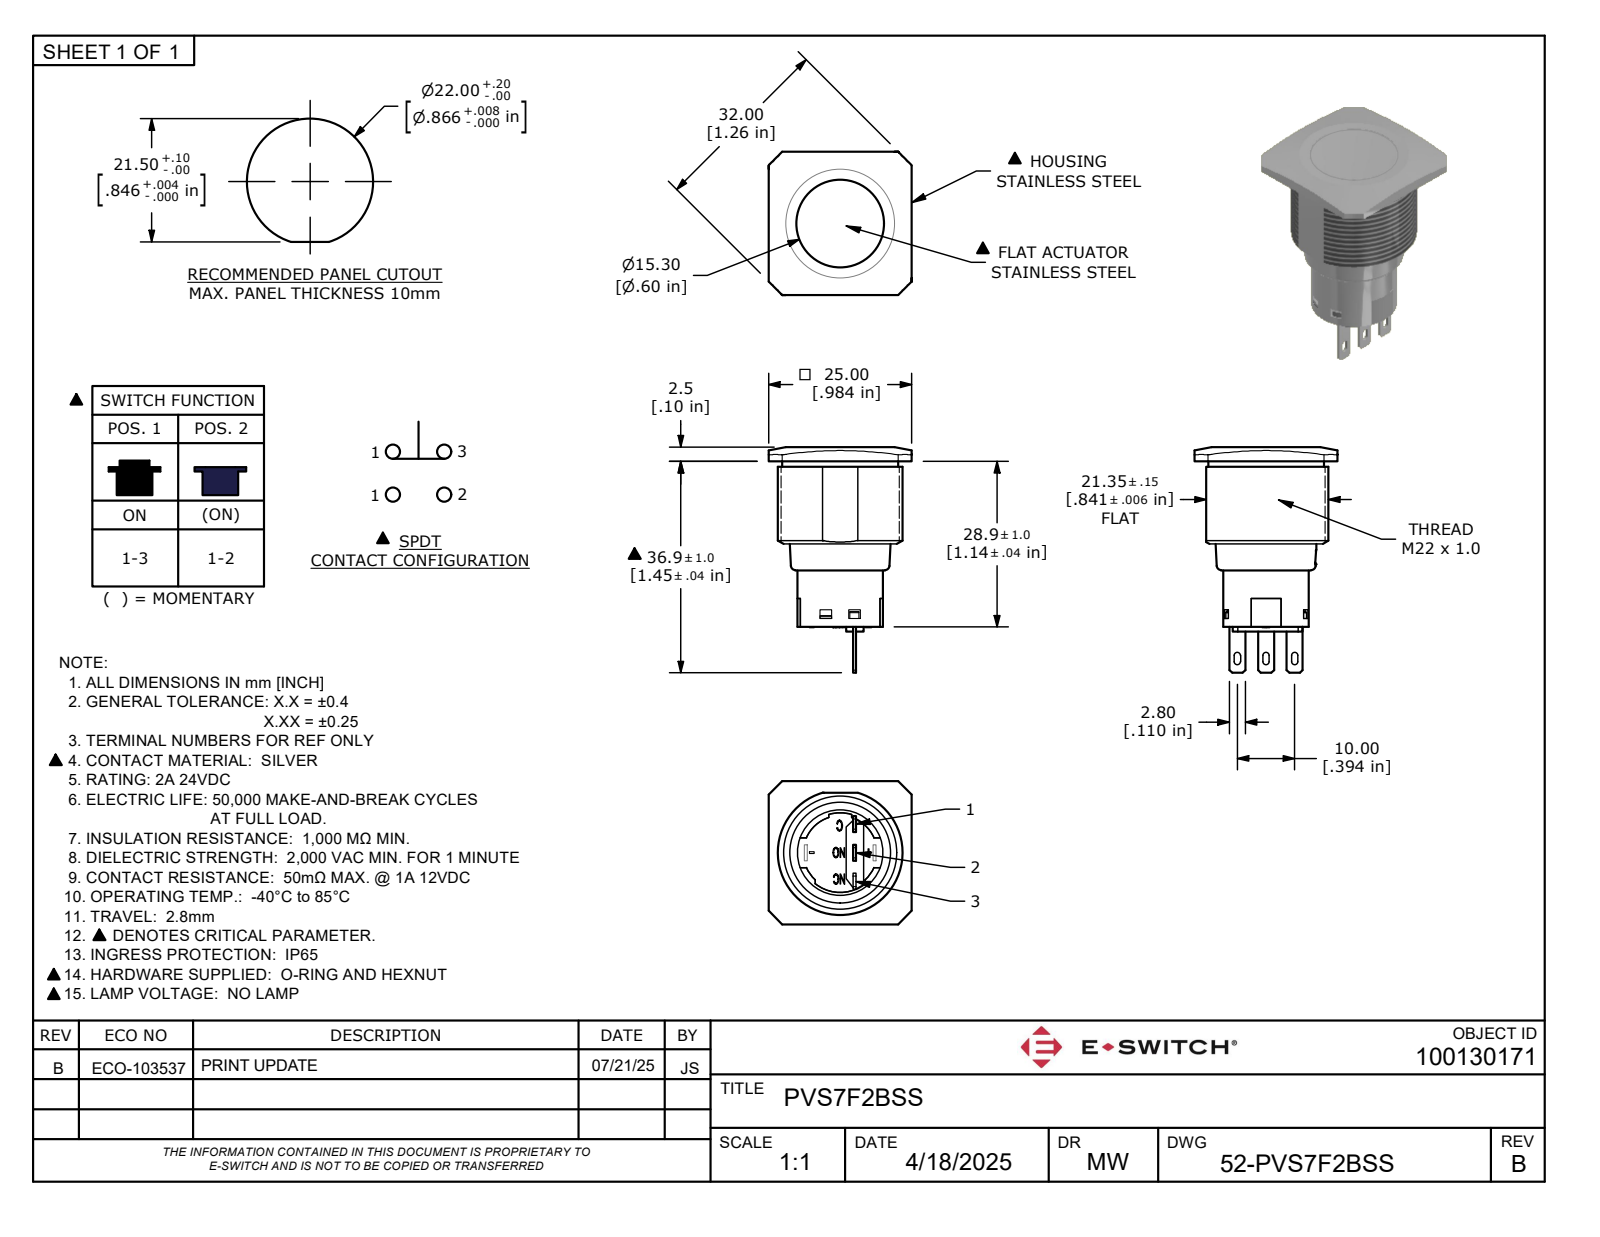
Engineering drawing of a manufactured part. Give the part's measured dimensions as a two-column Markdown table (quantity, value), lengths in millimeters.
| quantity | value |
| --- | --- |
| part name | 100130171_Simplify_1 |
| STEP written by | Autodesk Inventor 2022 (AUTOMOTIVE_DESIGN) |
| units | millimeters |
| bodies | 1 solid, 209 faces (133 planar, 28 cylindrical, 48 other) |
| overall size | 39.4 × 25 × 25 |
| volume | 9 470 mm³ |
| surface area | 3 415 mm² |
| round holes (diameter × count) | 15.3 × 1 |
| round bosses / shafts (diameter × count) | 21.8 × 1, 20.2 × 1, 14.9 × 1 |
| partial cylindrical surfaces (radius × count) | 0.2 × 8, 0.6 × 6, 6.5 × 1, 7 × 1, 7.2 × 1 |
| main face-to-face distances | 2.5, 31.4, 28.9, 2.5, 31.4, 25, 14.5, 16.9, 16.9, 14.4 |
